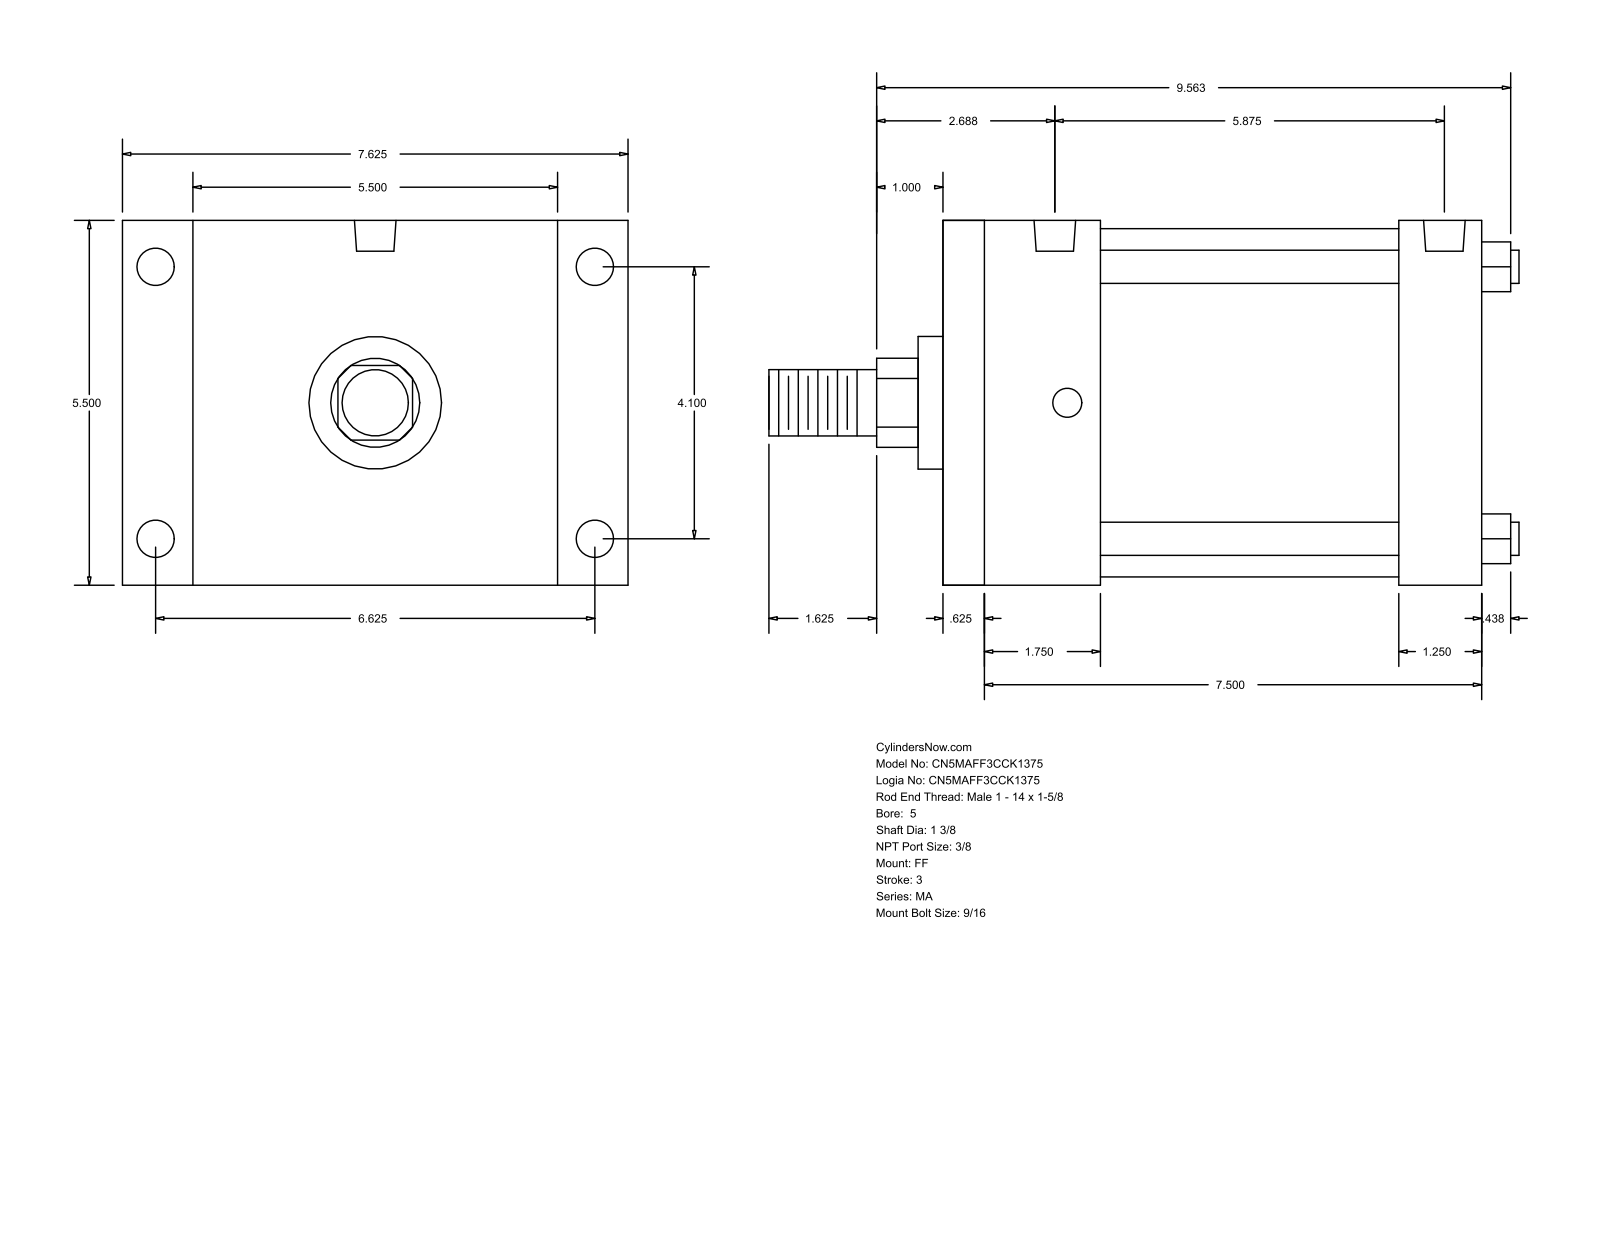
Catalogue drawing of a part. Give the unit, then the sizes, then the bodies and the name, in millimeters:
Units: millimetres
Overall size (bounding box): 287.34 × 193.68 × 139.7
Round holes (diameter × count): ⌀11.11 ×4, ⌀14.29 ×4, ⌀15.93 ×2
Round bosses / shafts (diameter × count): ⌀12.7 ×4, ⌀133.35 ×1, ⌀50.8 ×1, ⌀34.92 ×1, ⌀25.4 ×1
Partial cylindrical surfaces — rounded edges, fillets, slot ends (radius × count): R17.06 ×1
Main face-to-face distances: 139.7, 206.38, 15.87, 190.51, 174.63, 158.76, 31.75, 60.32, 44.45, 114.31
Hole centre spacings: 4.77, 104.14, 139.69, 144.46, 168.28, 197.9, 149.23
Bodies: 0 solids, 92 faces (64 planar, 28 cylindrical, 0 other)
Part name (STEP PRODUCT): MA_FF__0500_1.375
STEP written by: GSSL Pune (CONFIG_CONTROL_DESIGN)
